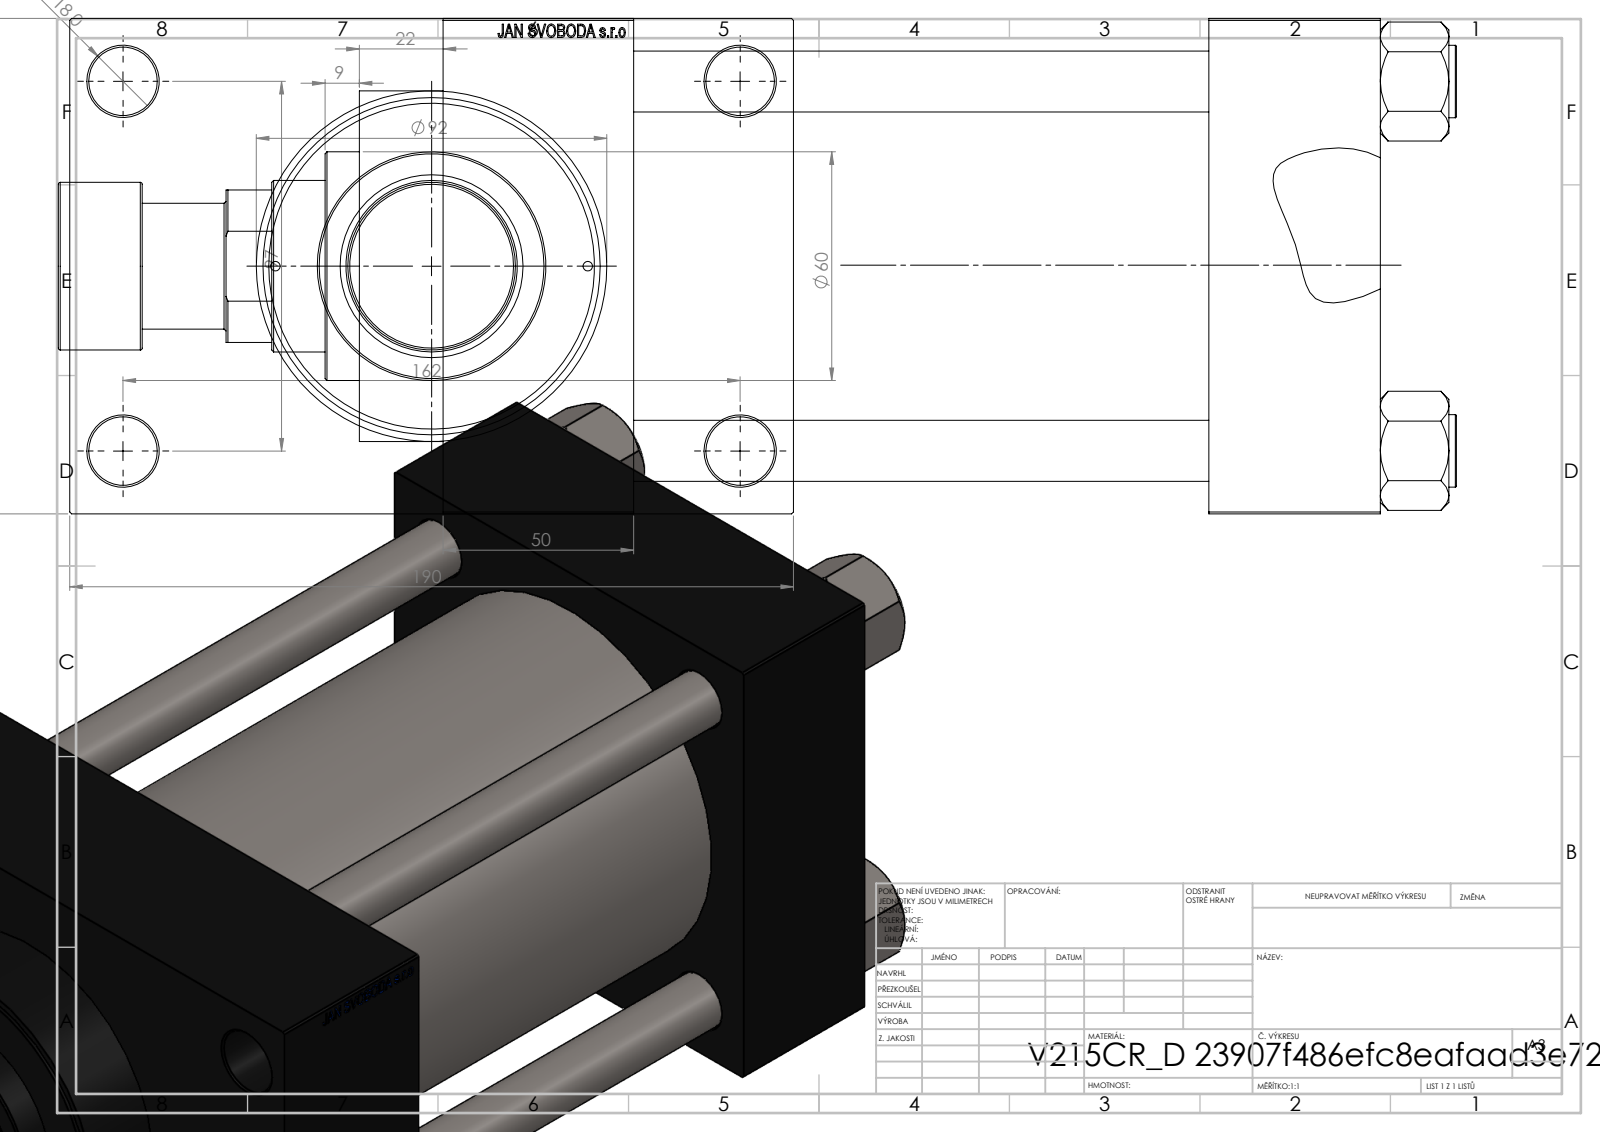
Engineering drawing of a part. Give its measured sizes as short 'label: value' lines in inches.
name: NUT_M5_D; V215CR_D_TYCINKA; V215CR_D_Body; V215_VC_A (+2 more)
written by: SolidWorks 2019 (CONFIG_CONTROL_DESIGN)
unit: in
bodies: 12 solids, 1172 faces (550 planar, 96 cylindrical, 526 other)
size: 14.449 × 7.48 × 5.118
volume: 177.7 in³; area: 685.5 in²
holes: 4× ⌀0.63, 4× ⌀0.709, 2× ⌀0.098, 2× ⌀0.276, 2× ⌀1.041, 2× ⌀1.378, 1× ⌀1.24, 1× ⌀1.772, 1× ⌀1.89, 1× ⌀2.992, 1× ⌀3.366, 1× ⌀3.937
bosses: 4× ⌀0.748, 1× ⌀4.173, 1× ⌀3.622, 1× ⌀2.362, 1× ⌀1.732, 1× ⌀1.299
face distances: 5.118, 5.945, 1.772, 7.717, 9.685, 7.913, 1.969, 1.181, 6.299, 3.78
hole spacings: 1.281, 1.93, 2.475, 2.698, 3.717, 3.815, 4.005, 4.026
